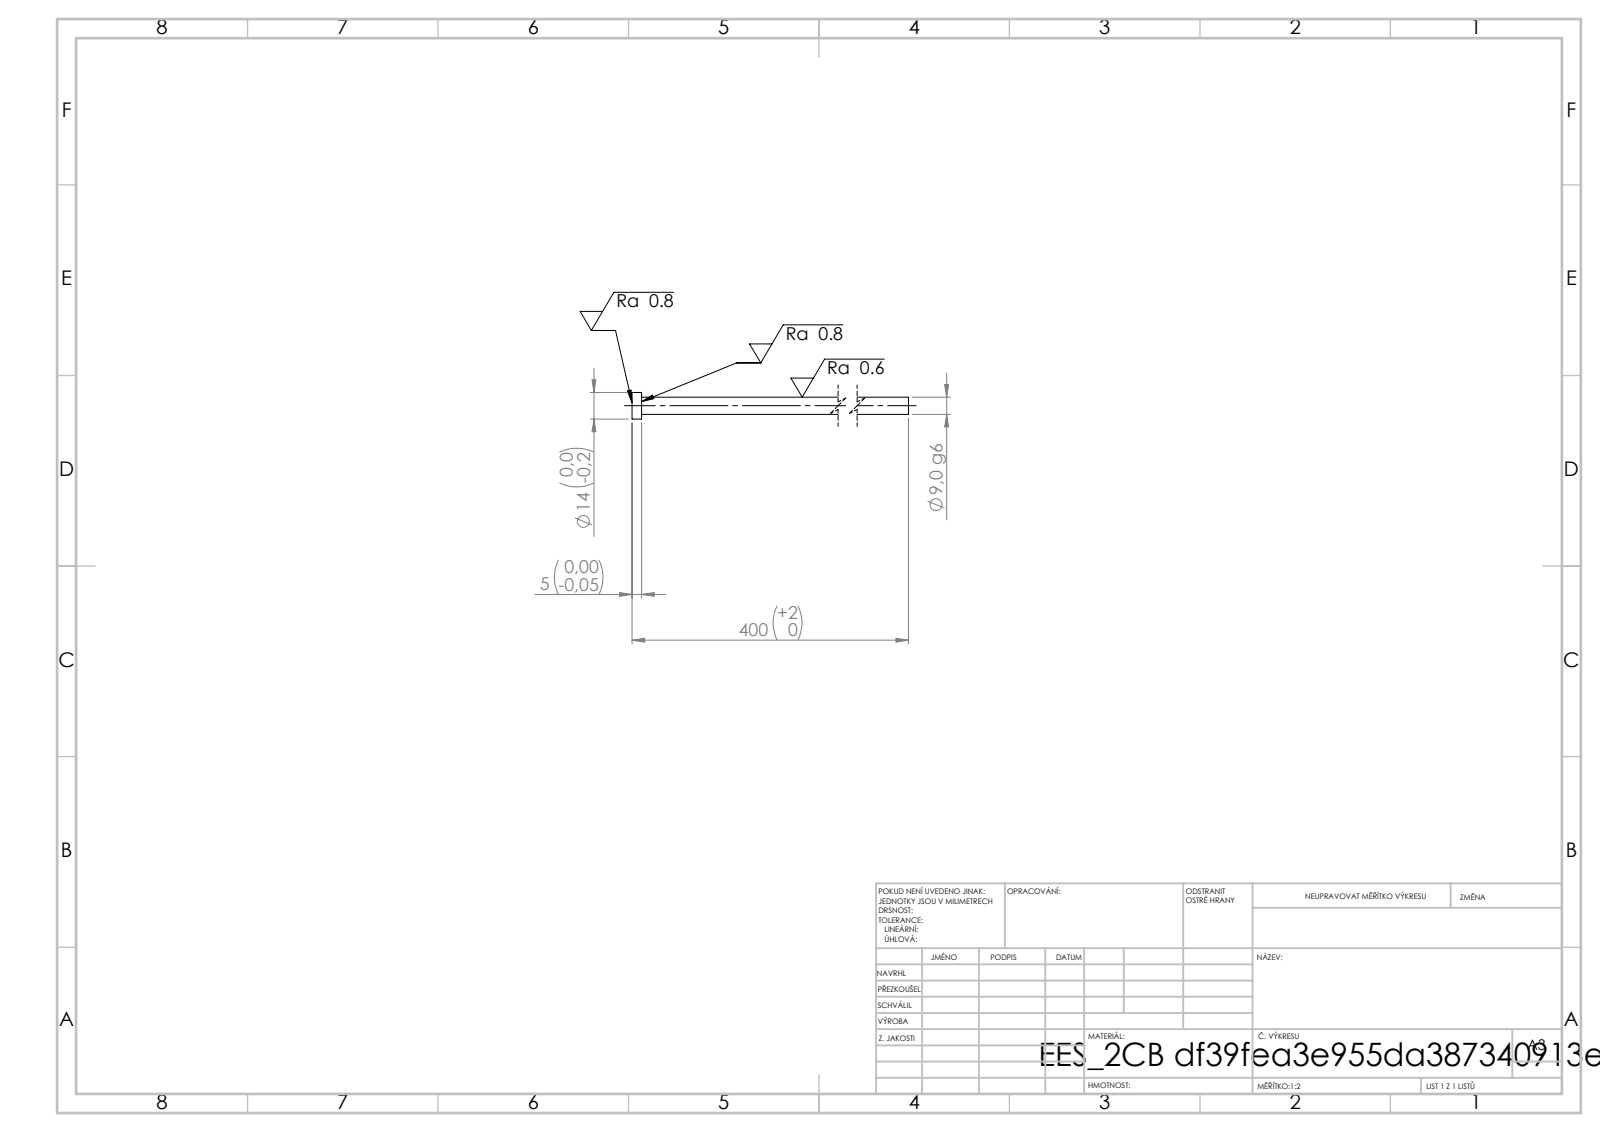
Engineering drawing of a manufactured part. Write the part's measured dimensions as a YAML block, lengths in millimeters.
step_written_by: "SolidWorks 2019 (CONFIG_CONTROL_DESIGN)"
units: millimeters
bodies: {solids: 1, faces: 7, planar: 3, cylindrical: 4, other: 0}
overall_size: [400, 14, 14]
volume: 25899
surface_area: 11696
round_bosses_or_shafts:
  - {diameter: 14, count: 1}
  - {diameter: 9, count: 1}
face_to_face_distances: [5, 400, 395]
